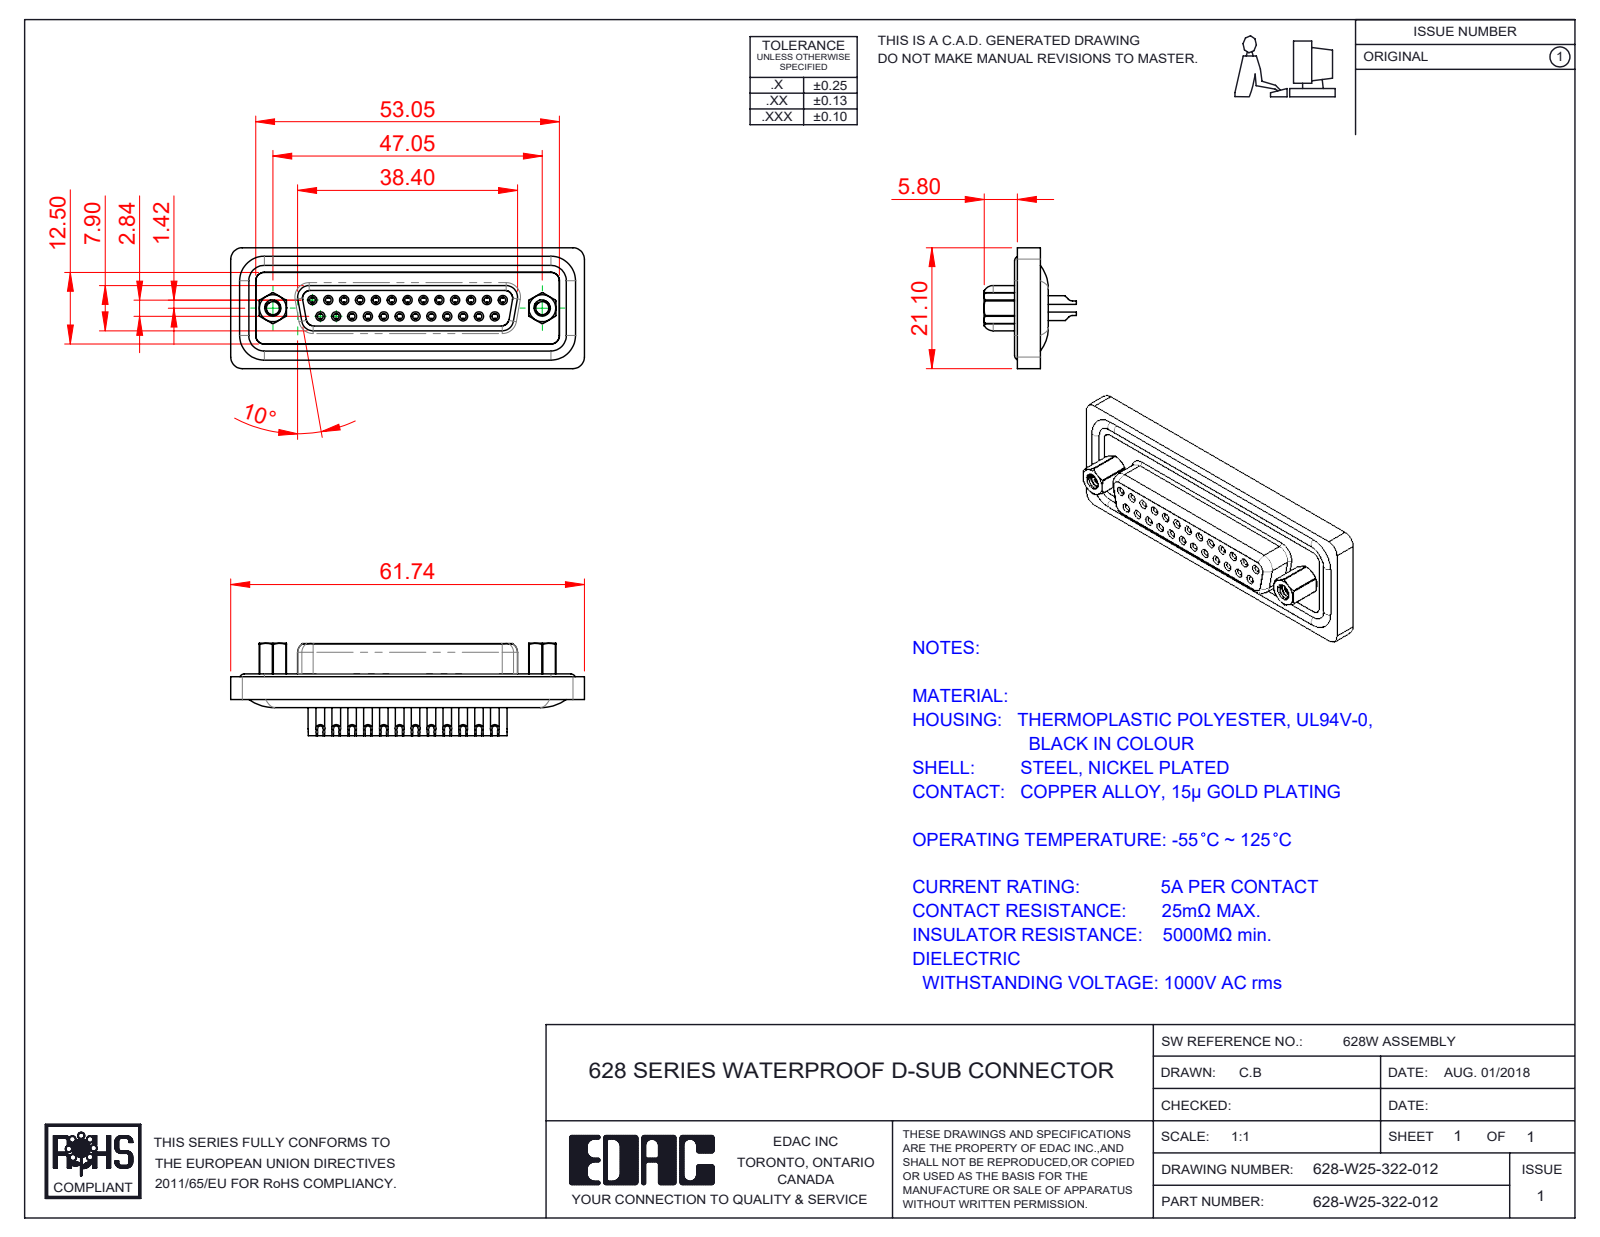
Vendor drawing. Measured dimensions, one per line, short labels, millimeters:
name: 628W 4-40 Hex Standoff; 628W Contact Row 2_22; 628-W25-322-012; 628W Shell Front_25 Contacts (+4 more)
written by: SolidWorks 2020 (CONFIG_CONTROL_DESIGN)
unit: mm
bodies: 33 solids, 1848 faces (526 planar, 795 cylindrical, 527 other)
size: 61.5 × 21.1 × 16.1
volume: 8 513 mm³; area: 13 570 mm²
holes: 25× ⌀1, 25× ⌀1.1, 25× ⌀1.5, 25× ⌀1.7, 25× ⌀1.8, 25× ⌀2, 2× ⌀2.26, 2× ⌀2.29, 2× ⌀4, 2× ⌀4.8, 2× ⌀5
bosses: 29× ⌀1.6, 25× ⌀2.2, 2× ⌀4.9, 2× ⌀2.79
rounds: 16× R2, 14× R1.5, 8× R1.35, 6× R2.7, 4× R0.5, 4× R0.9, 4× R1.6, 4× R1.75
face distances: 0.4, 7.45, 1.1, 2.75, 7.5, 13.65, 0.5, 8.45, 3.75, 6.2
hole spacings: 3.16, 2.77, 5.54, 8.31, 11.08, 13.85, 16.62, 5.03
